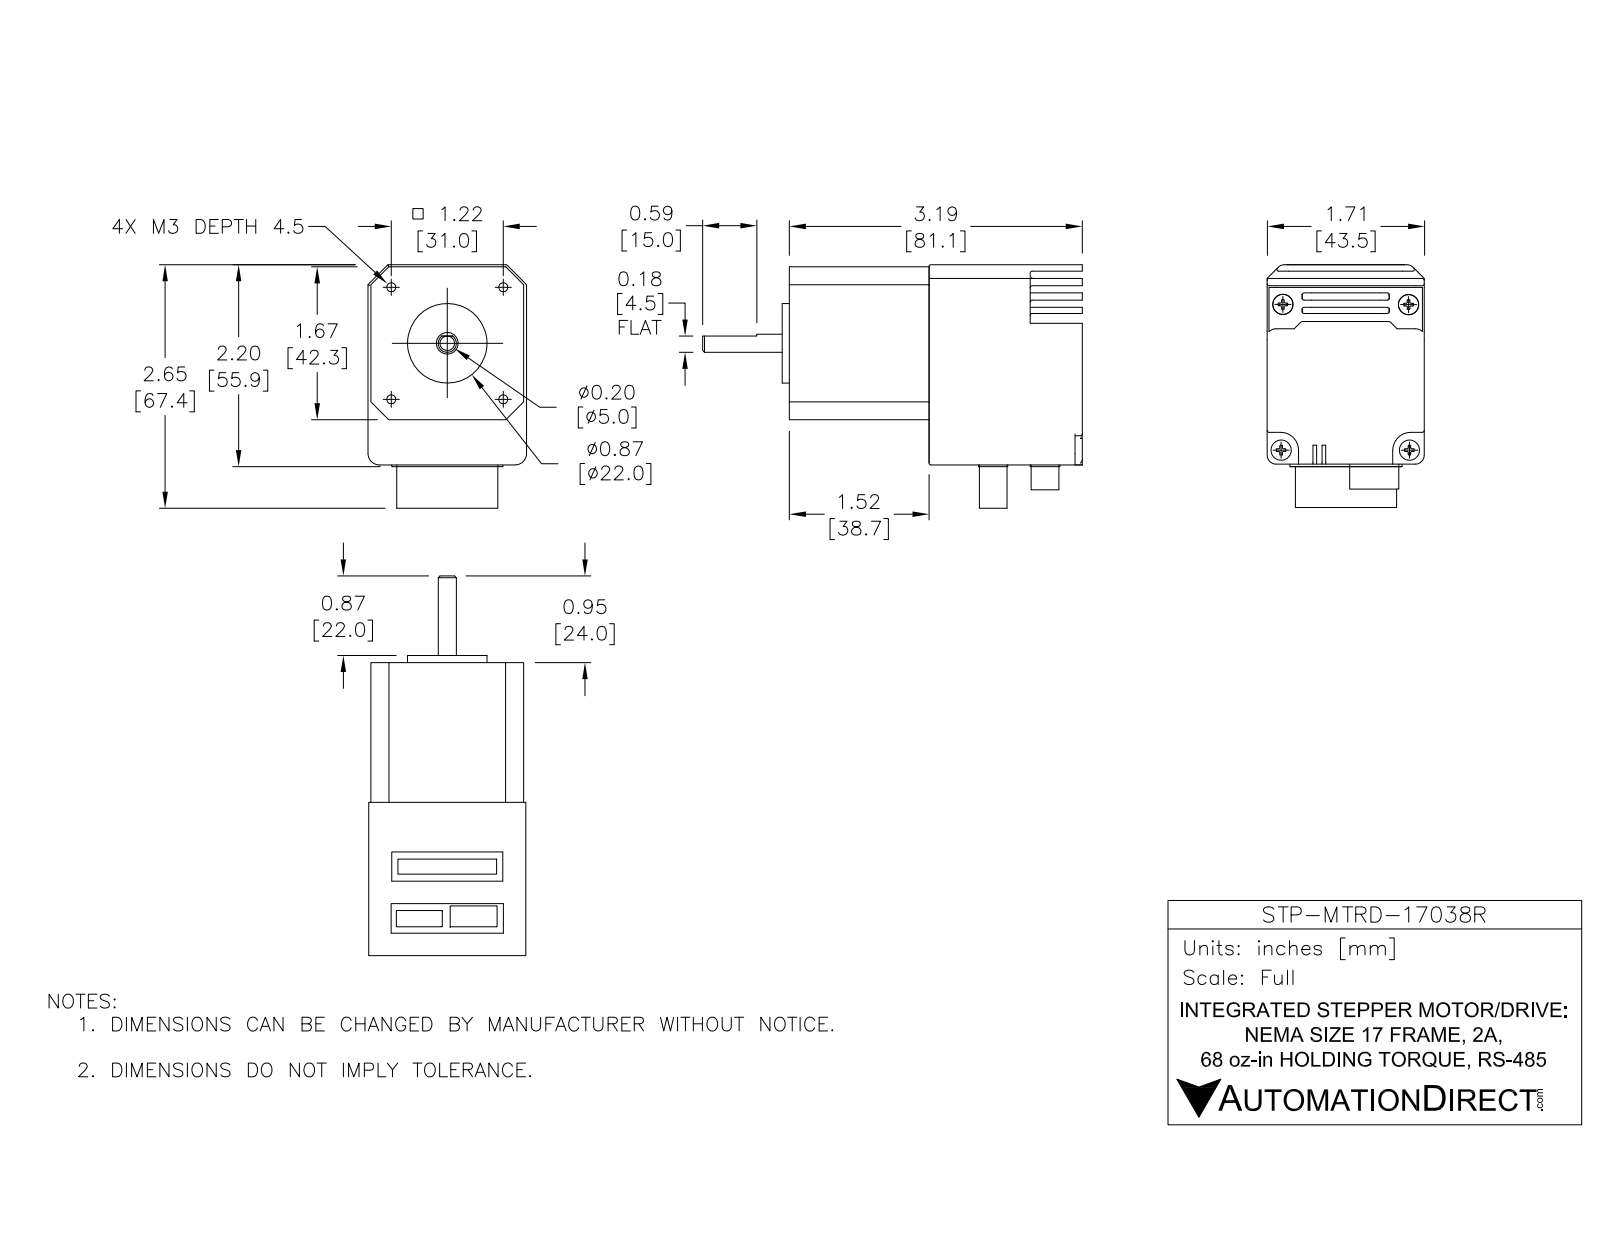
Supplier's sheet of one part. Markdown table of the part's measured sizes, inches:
| quantity | value |
| --- | --- |
| part name | STP-MTRD-17038R |
| STEP written by | SolidWorks 2017 (AUTOMOTIVE_DESIGN) |
| units | inches |
| bodies | 2 solids, 396 faces (149 planar, 156 cylindrical, 91 other) |
| overall size | 4.138 × 2.199 × 1.713 |
| volume | 9.507 in³ |
| surface area | 37.79 in² |
| round holes (diameter × count) | 0.118 × 4, 0.295 × 1, 0.591 × 1 |
| round bosses / shafts (diameter × count) | 0.22 × 4, 0.866 × 1, 0.197 × 1 |
| partial cylindrical surfaces (radius × count) | 0.02 × 75, 0.098 × 12, 0.027 × 4, 0.431 × 4, 0.999 × 4, 0.197 × 2, 0.03 × 1 |
| main face-to-face distances | 0.071, 0.079, 1.642, 1.571, 1.713, 3.193, 0.157, 1.618, 0.047, 2.173 |
| hole center spacings | 0.863, 1.22, 1.726 |
